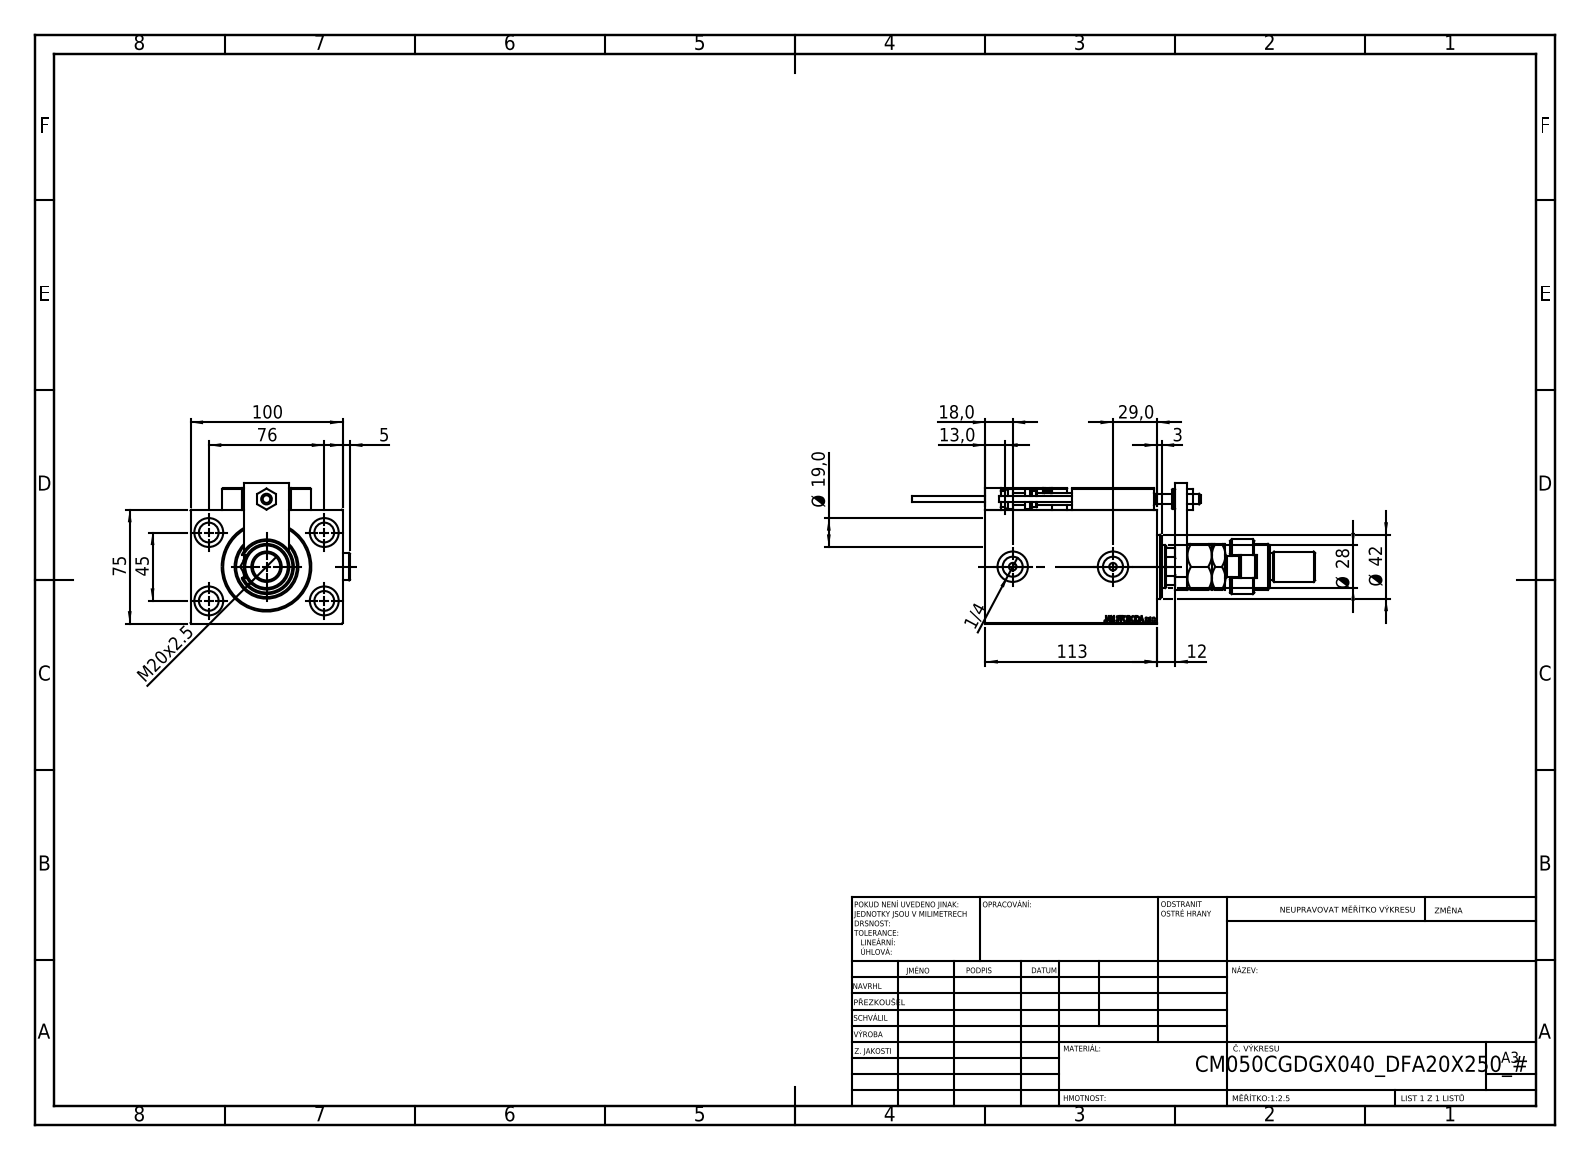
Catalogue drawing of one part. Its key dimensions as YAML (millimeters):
part_name: "ALLEN BOLT D8; SWITCH DIM B,W; V450CM_C_Body; SWITCH_X_FRONT_BACK (+8 more)"
step_written_by: "SolidWorks 2019 (CONFIG_CONTROL_DESIGN)"
units: millimeters
bodies: {solids: 27, faces: 1424, planar: 623, cylindrical: 219, other: 582}
overall_size: [265, 104.9, 92.5]
volume: 818671
surface_area: 160208
round_holes:
  - {diameter: 8, count: 5}
  - {diameter: 3.2, count: 4}
  - {diameter: 4, count: 4}
  - {diameter: 5, count: 4}
  - {diameter: 13, count: 4}
  - {diameter: 19, count: 4}
  - {diameter: 20, count: 3}
  - {diameter: 13.16, count: 2}
  - {diameter: 7, count: 1}
  - {diameter: 18.5, count: 1}
  - {diameter: 28, count: 1}
  - {diameter: 31.5, count: 1}
round_bosses_or_shafts:
  - {diameter: 18, count: 3}
  - {diameter: 5, count: 2}
  - {diameter: 3.8, count: 2}
  - {diameter: 42, count: 1}
  - {diameter: 36, count: 1}
  - {diameter: 30, count: 1}
  - {diameter: 22, count: 1}
  - {diameter: 14, count: 1}
partial_cylinders:
  - {radius: 0.3, count: 30}
  - {radius: 3, count: 2}
  - {radius: 7.5, count: 1}
  - {radius: 12, count: 1}
  - {radius: 13.5, count: 1}
face_to_face_distances: [75, 100, 14, 113, 12, 99, 20, 87, 8, 24]
hole_center_spacings: [44.16, 11.37, 20, 29.59, 29.69, 36.06, 42.19, 43.91]
